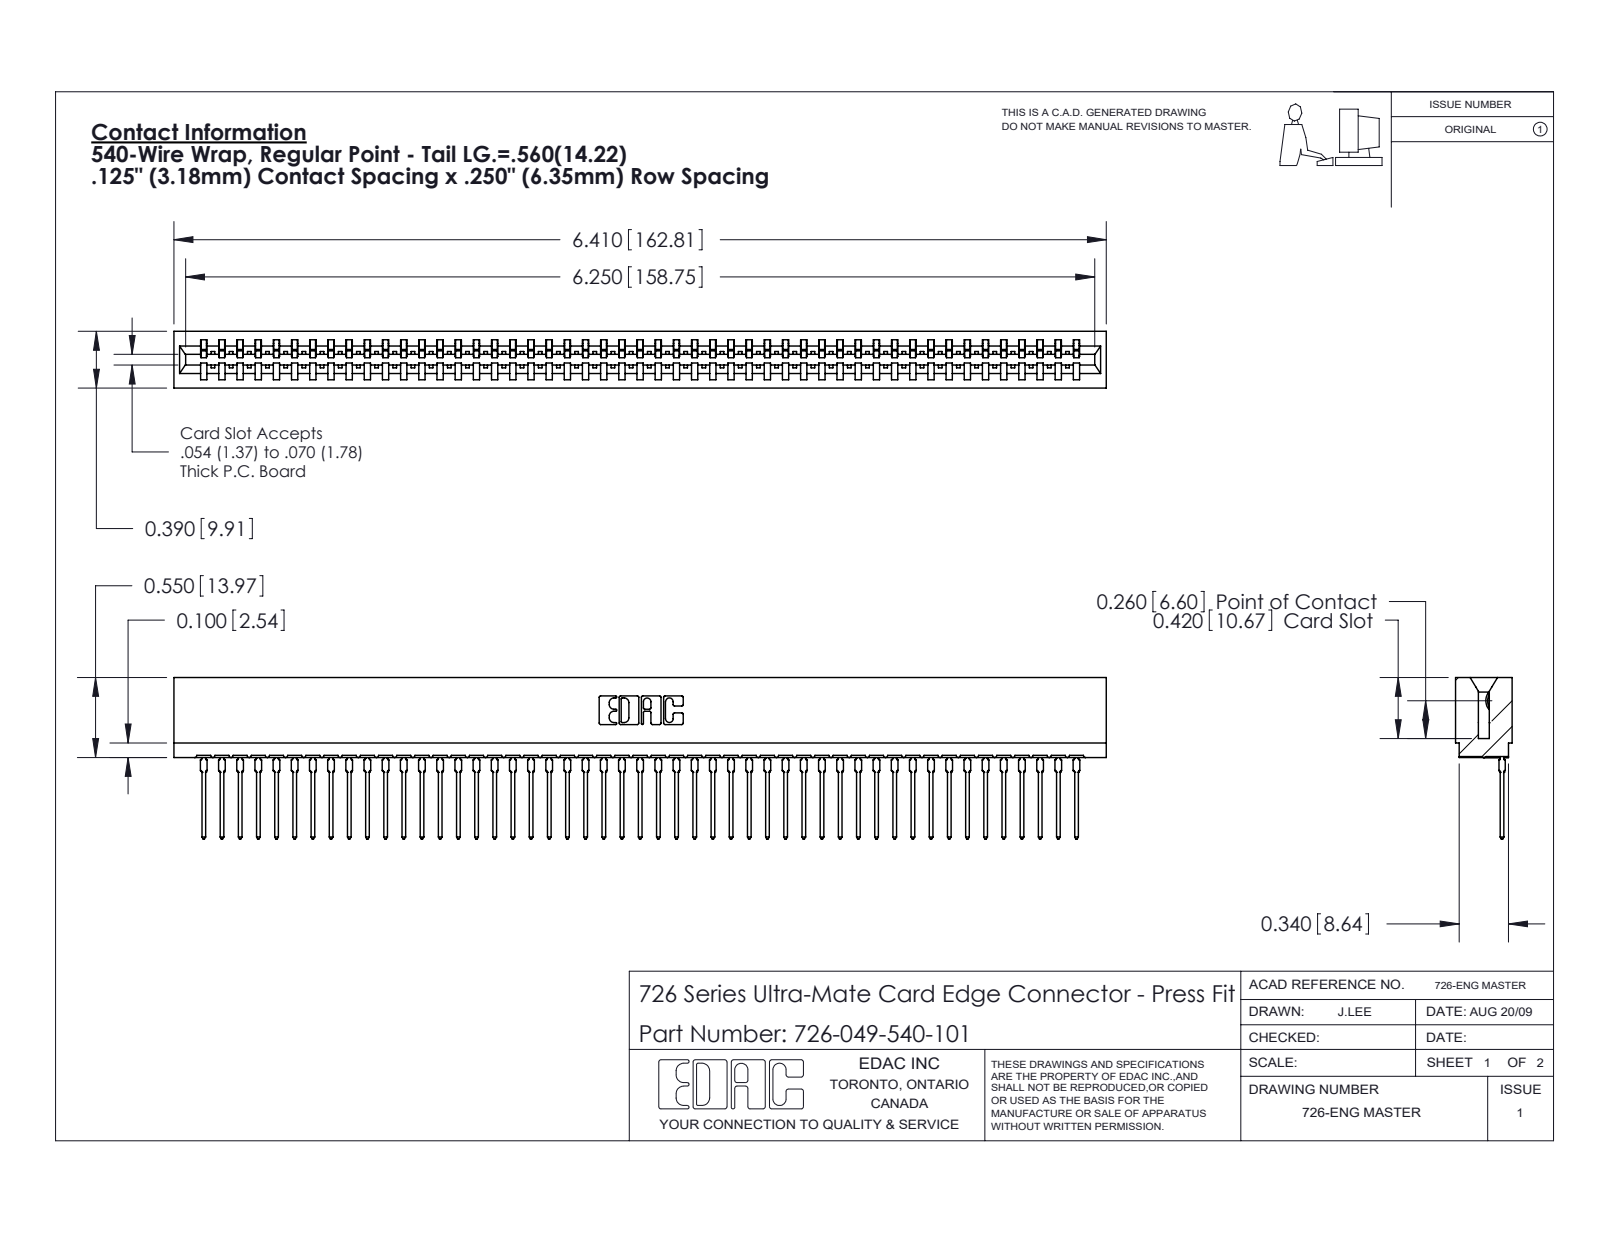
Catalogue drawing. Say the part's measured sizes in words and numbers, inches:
The part is named "726 Part_.515 Slot Depth - 01; 746-292-001_540; 726-049-540-101". Its 3-D file was written by "SolidWorks 2020 (CONFIG_CONTROL_DESIGN)". It is 50 solids with 5389 faces: 3142 planar, 973 cylindrical and 1274 other. Overall it measures 6.41 by 1.109 by 0.39 inches. Its volume is 0.892 cubic inches and its surface area 35.64 square inches. Partial cylindrical surfaces (rounded edges, fillets, slot ends): 98 of radius 0.021, 50 of radius 0.015, 22 of radius 0.01, 6 of radius 0.007, 6 of radius 0.031, 4 of radius 0.005, 4 of radius 0.011, 3 of radius 0.026. The main face-to-face distances are 0.057, 0.333, 0.39, 0.025, 0.307, 0.25, 0.083, 0.275, 0.365, 0.032.
